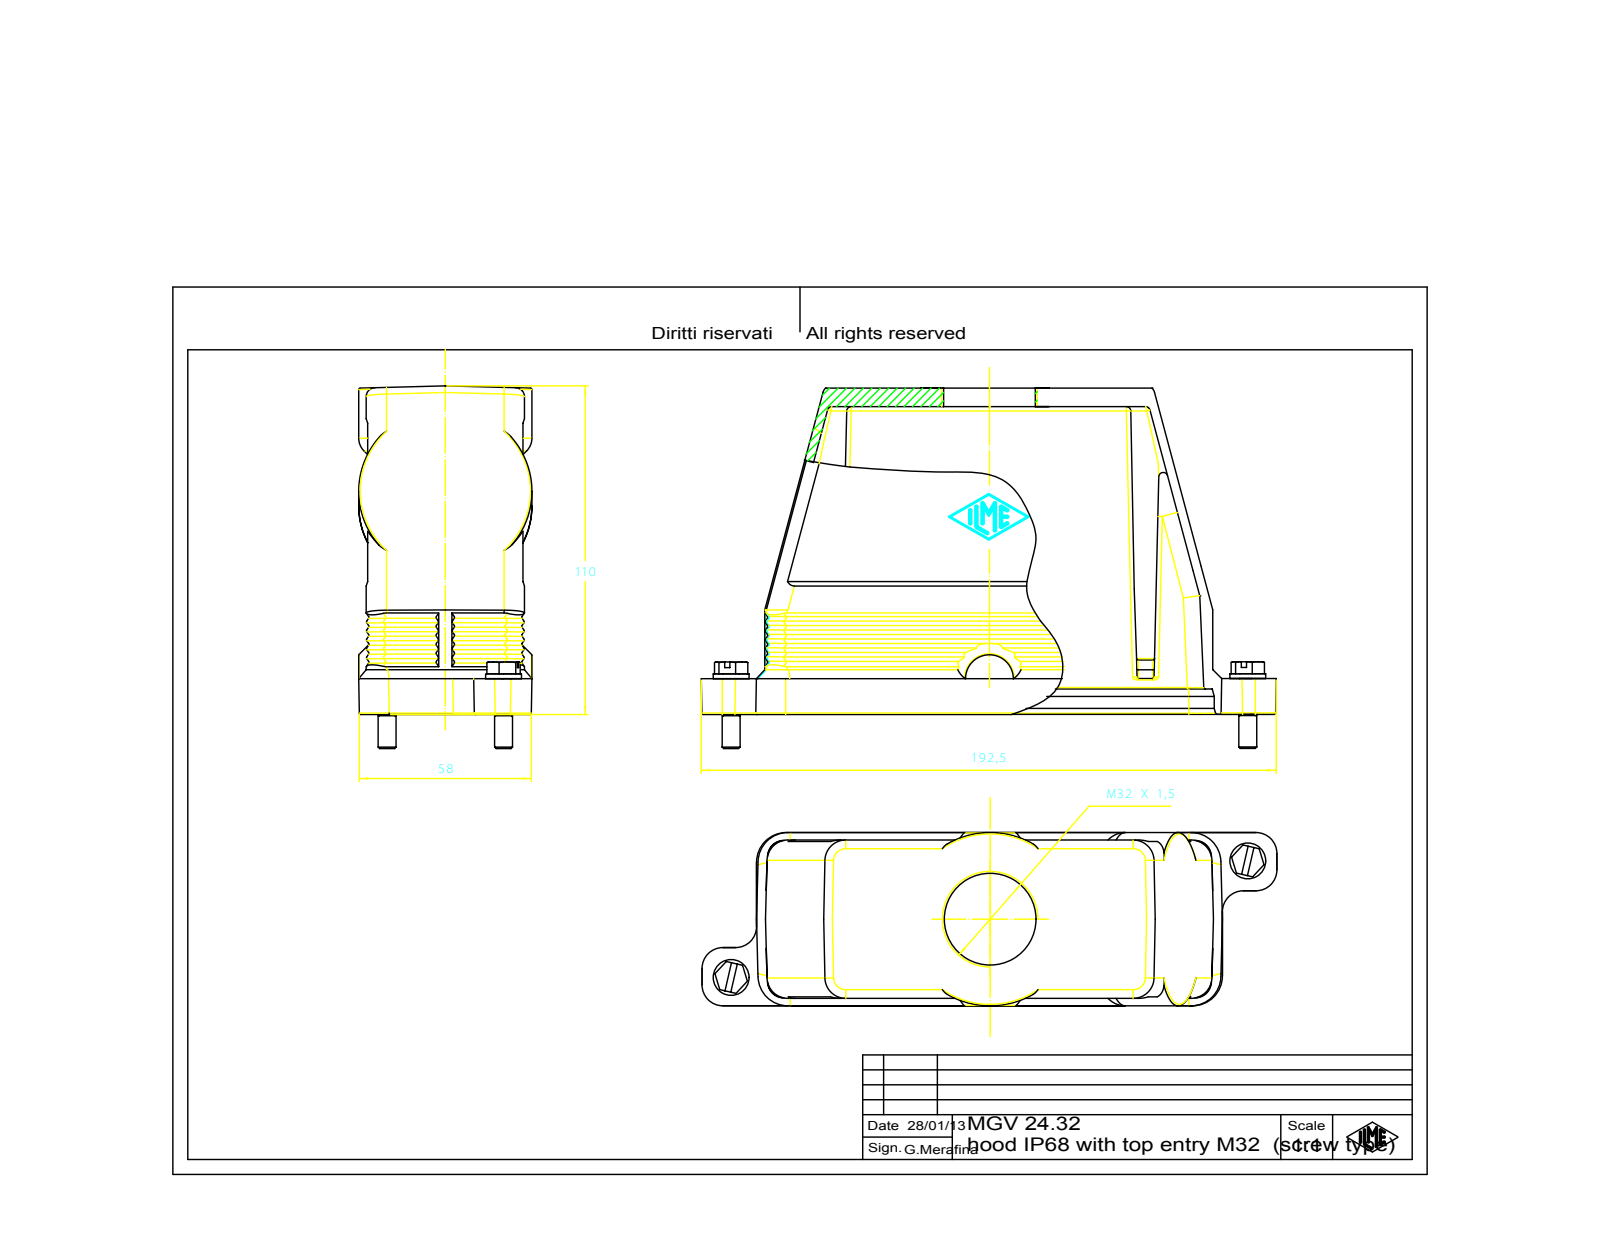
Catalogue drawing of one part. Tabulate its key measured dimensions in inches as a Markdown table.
| quantity | value |
| --- | --- |
| part name | MGV 24.32 |
| STEP written by | Autodesk Inventor 7 (AUTOMOTIVE_DESIGN) |
| units | inches |
| bodies | 3 solids, 767 faces (189 planar, 195 cylindrical, 383 other) |
| overall size | 7.579 × 4.811 × 2.283 |
| volume | 15.65 in³ |
| surface area | 166.6 in² |
| round holes (diameter × count) | 0.097 × 2, 0.126 × 2, 0.26 × 2, 0.591 × 2, 1.26 × 1 |
| round bosses / shafts (diameter × count) | 2.283 × 2, 2.205 × 2, 0.492 × 2, 0.236 × 2 |
| partial cylindrical surfaces (radius × count) | 0.02 × 39, 0.03 × 14, 0.295 × 8, 0.236 × 6, 0.059 × 4, 0.118 × 4, 0.226 × 2, 0.413 × 2 |
| main face-to-face distances | 0.118, 2.047, 1.929, 1.811, 0.236, 2.165, 0.098, 0.02, 2.283, 0.138 |
| hole center spacings | 1.385, 5.611, 4.23, 6.993 |
